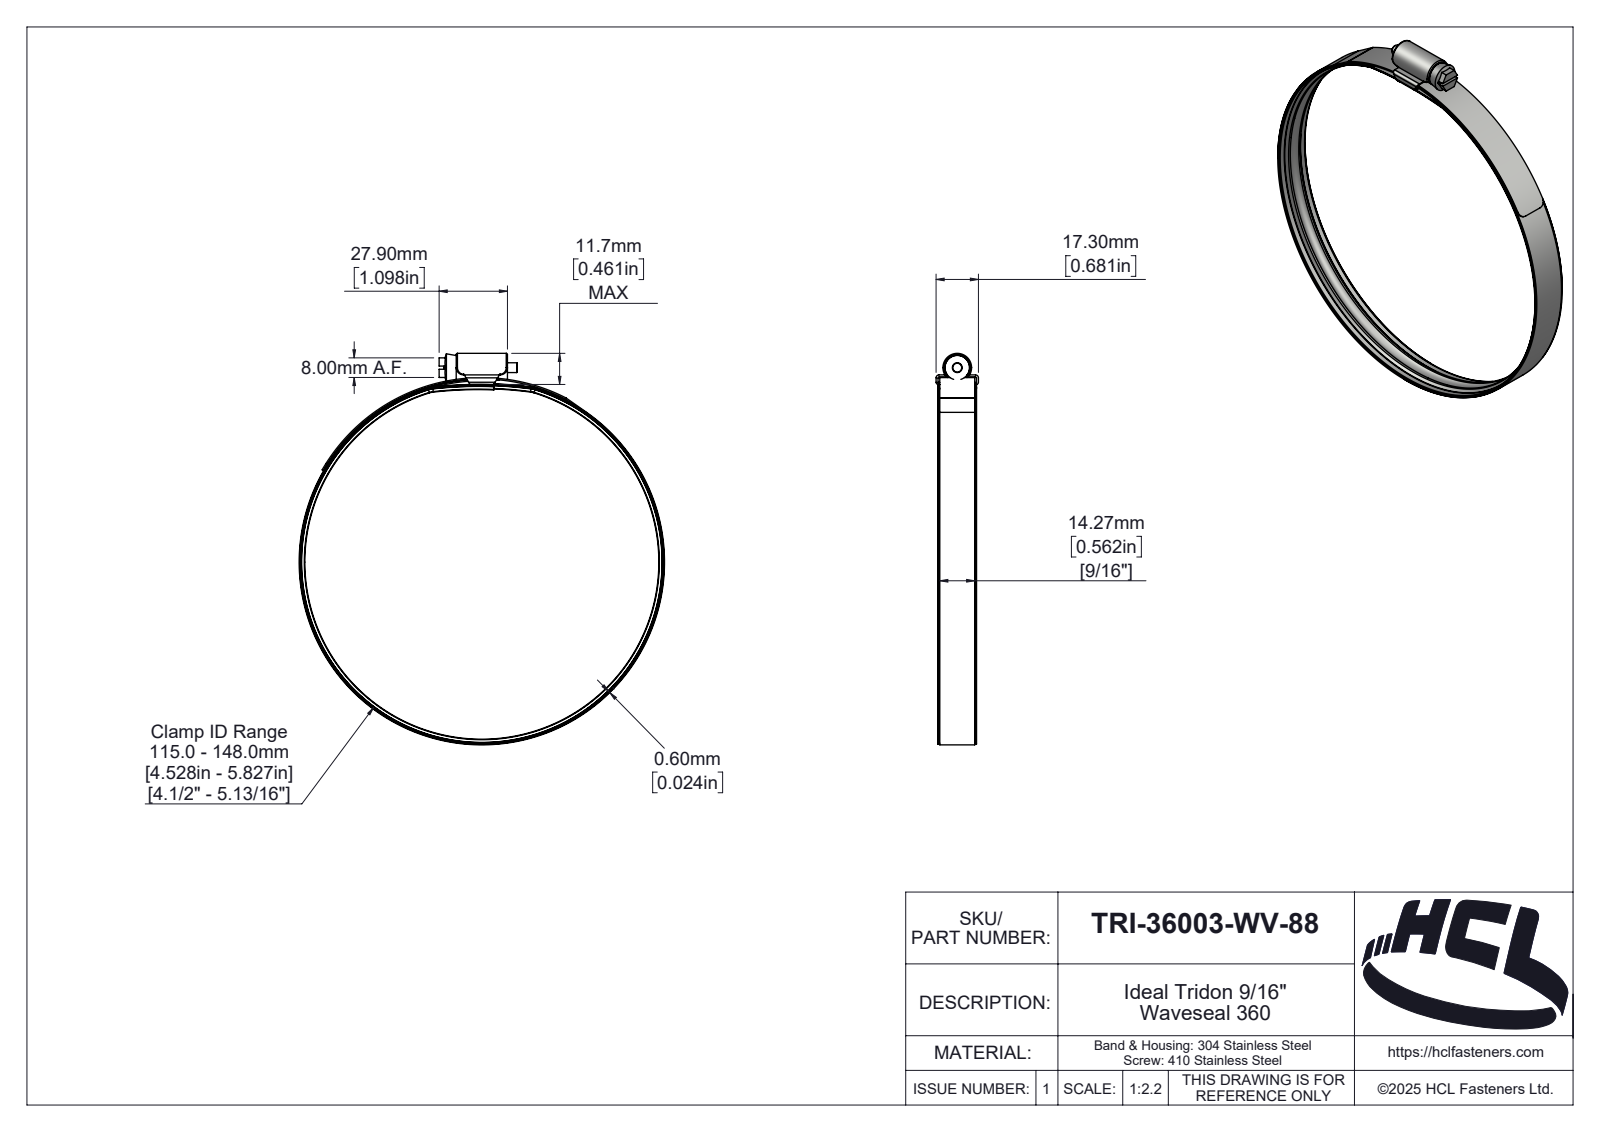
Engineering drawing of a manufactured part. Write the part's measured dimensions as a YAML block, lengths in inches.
part_name: "TRI-36003-WV-88"
step_written_by: "SolidWorks 2025 (AUTOMOTIVE_DESIGN)"
units: inches
bodies: {solids: 4, faces: 418, planar: 42, cylindrical: 119, other: 257}
overall_size: [6.291, 5.874, 0.681]
volume: 0.56
surface_area: 55.5
round_holes:
  - {diameter: 5.803, count: 1}
  - {diameter: 5.827, count: 1}
round_bosses_or_shafts:
  - {diameter: 5.874, count: 1}
  - {diameter: 5.819, count: 1}
  - {diameter: 0.394, count: 1}
  - {diameter: 0.157, count: 1}
partial_cylinders:
  - {radius: 0.02, count: 6}
  - {radius: 0.118, count: 4}
  - {radius: 0.004, count: 2}
  - {radius: 0.035, count: 2}
  - {radius: 0.047, count: 2}
  - {radius: 0.39, count: 2}
  - {radius: 0.398, count: 2}
  - {radius: 0.018, count: 1}
face_to_face_distances: [0.561, 0.031, 0.122, 0.024, 0.091, 0.154, 1.098, 0.06, 0.621, 0.65]
